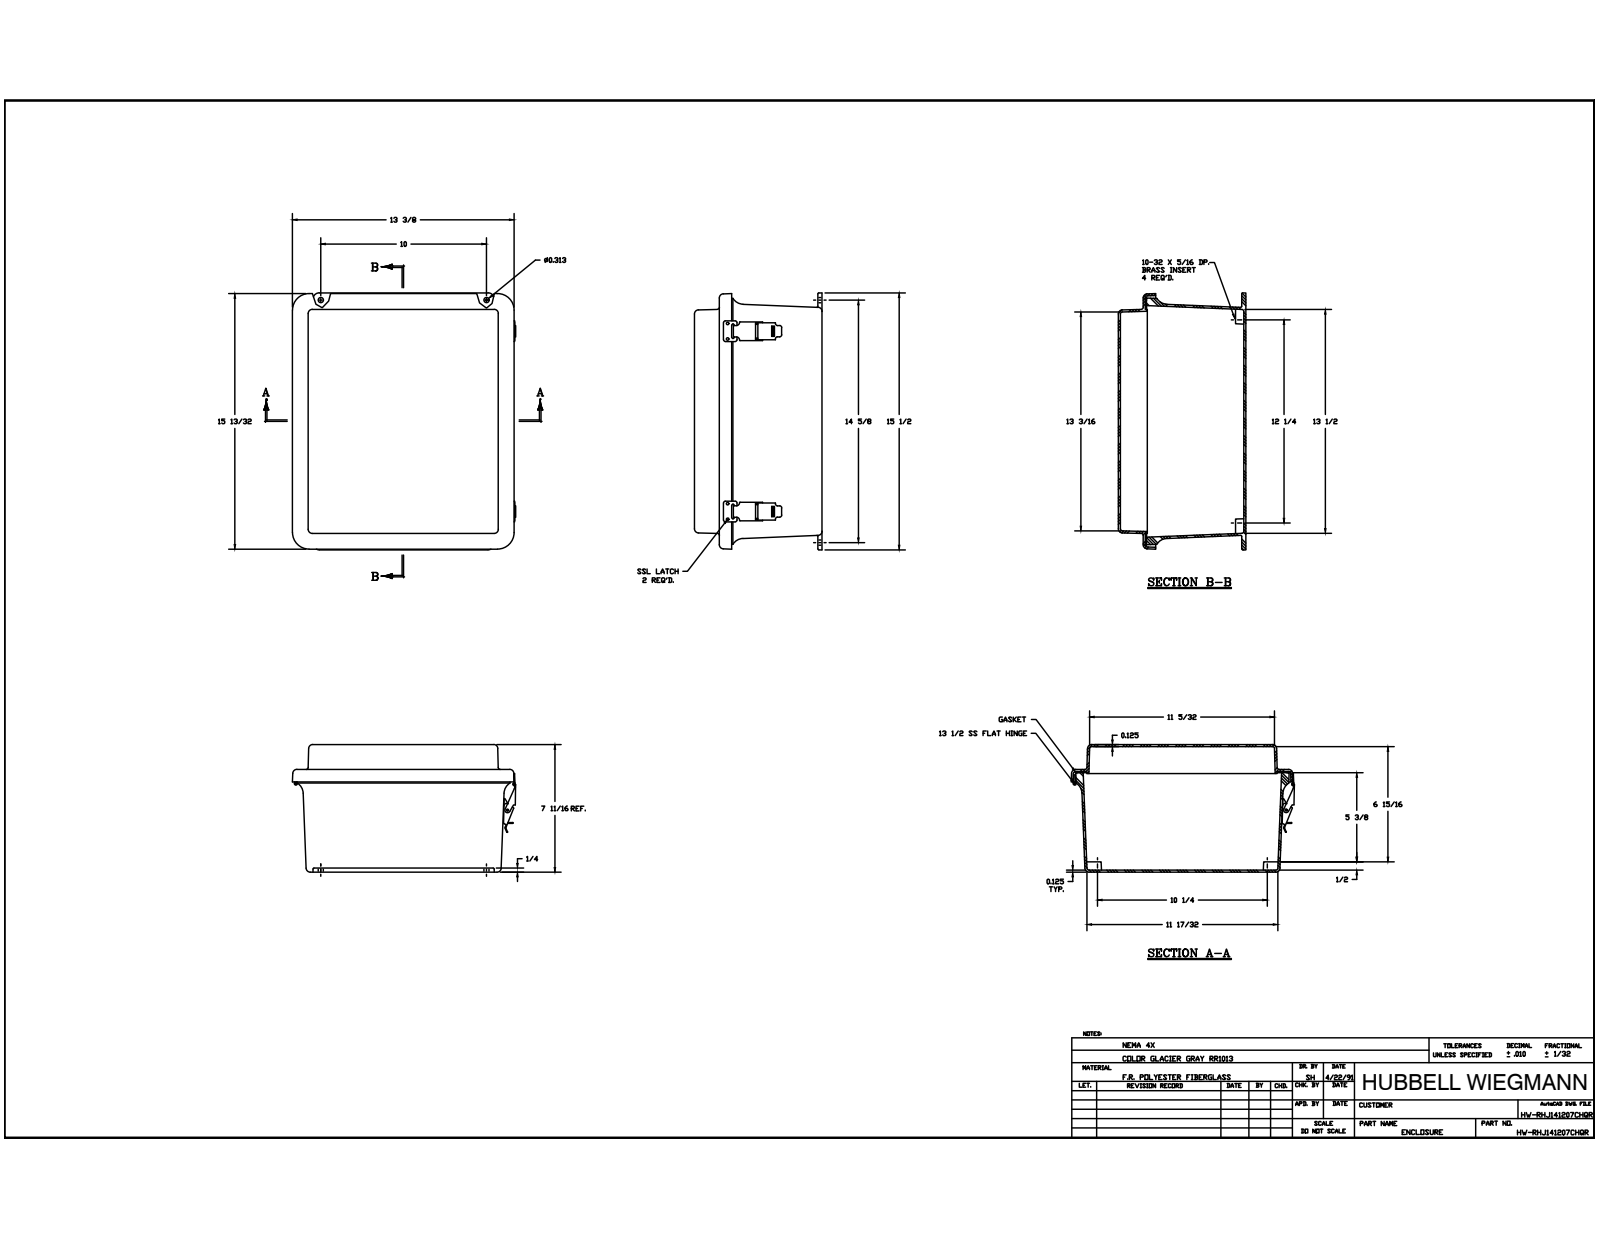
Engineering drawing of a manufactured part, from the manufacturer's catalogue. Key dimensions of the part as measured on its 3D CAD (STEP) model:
Part name (STEP PRODUCT): J1412HL_6; RMINS45821P_277; RMINS45821P_278; RMINS45821P_279 (+8 more)
STEP written by: Autodesk Inventor 2014 (AUTOMOTIVE_DESIGN)
Units: millimetres
Bodies: 38 solids, 1101 faces (474 planar, 456 cylindrical, 171 other)
Overall size (bounding box): 393.7 × 343.46 × 195.65
Volume: 1 958 000 mm³ · Surface area: 1 124 000 mm²
Round holes (diameter × count): ⌀3.56 ×22, ⌀3.33 ×10, ⌀2.64 ×8, ⌀3.86 ×8, ⌀3.3 ×4, ⌀3.96 ×4, ⌀5.54 ×4, ⌀3.43 ×2, ⌀9.52 ×2, ⌀2.16 ×1
Round bosses / shafts (diameter × count): ⌀3.17 ×16, ⌀6.35 ×8, ⌀6.86 ×4, ⌀7.62 ×1, ⌀4.31 ×1, ⌀3.94 ×1, ⌀3.05 ×1
Partial cylindrical surfaces — rounded edges, fillets, slot ends (radius × count): R3.17 ×28, R0.38 ×20, R0.79 ×20, R6.35 ×20, R1.14 ×16, R0.76 ×12, R0.57 ×9, R1.52 ×6
Main face-to-face distances: 3.18, 3.17, 189.3, 192.48, 195.65, 192.47, 38.1, 151.2, 154.38, 41.27
Hole centre spacings: 82.55, 165.1, 276.4, 6.35, 247.65, 276.39, 277.06, 76.2
